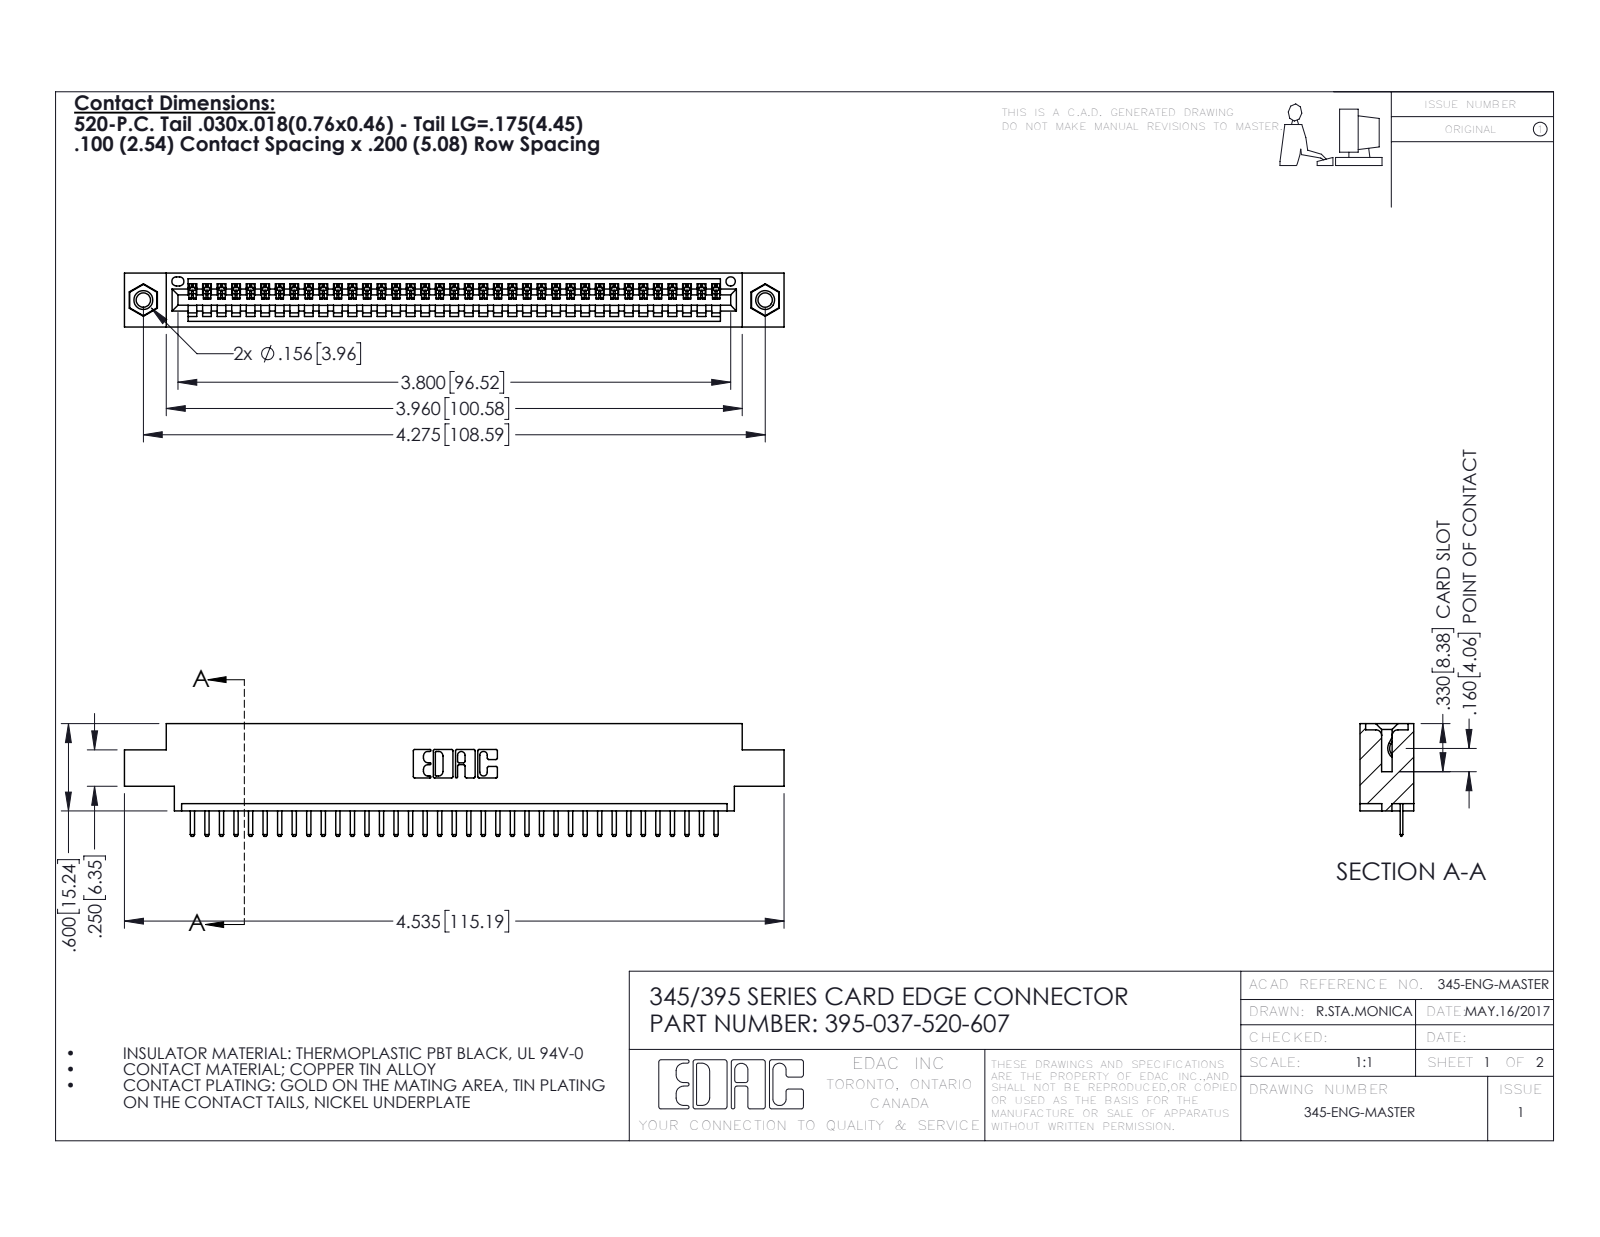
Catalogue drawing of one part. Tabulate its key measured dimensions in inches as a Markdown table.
| quantity | value |
| --- | --- |
| part name | 345-250-001_345-250-005-103; 345-292-001_345-293-120; 395-037-520-607; 345 Part_0.170 Offset - 0.156 Dia-TI |
| STEP written by | SolidWorks 2016 (CONFIG_CONTROL_DESIGN) |
| units | inches |
| bodies | 40 solids, 2484 faces (1670 planar, 798 cylindrical, 16 other) |
| overall size | 4.535 × 0.775 × 0.37 |
| volume | 0.651 in³ |
| surface area | 21.57 in² |
| round holes (diameter × count) | 0.098 × 2, 0.125 × 2, 0.156 × 2, 0.064 × 1 |
| round bosses / shafts (diameter × count) | 0.155 × 2 |
| partial cylindrical surfaces (radius × count) | 0.01 × 76, 0.006 × 74, 0.01 × 22, 0.007 × 6, 0.031 × 6, 0.026 × 3, 0.031 × 2, 0.04 × 2 |
| main face-to-face distances | 0.072, 0.298, 0.37, 0.2, 0.098, 0.272, 0.025, 0.225, 0.072, 0.175 |
| hole center spacings | 0.27, 4.039, 4.275 |
